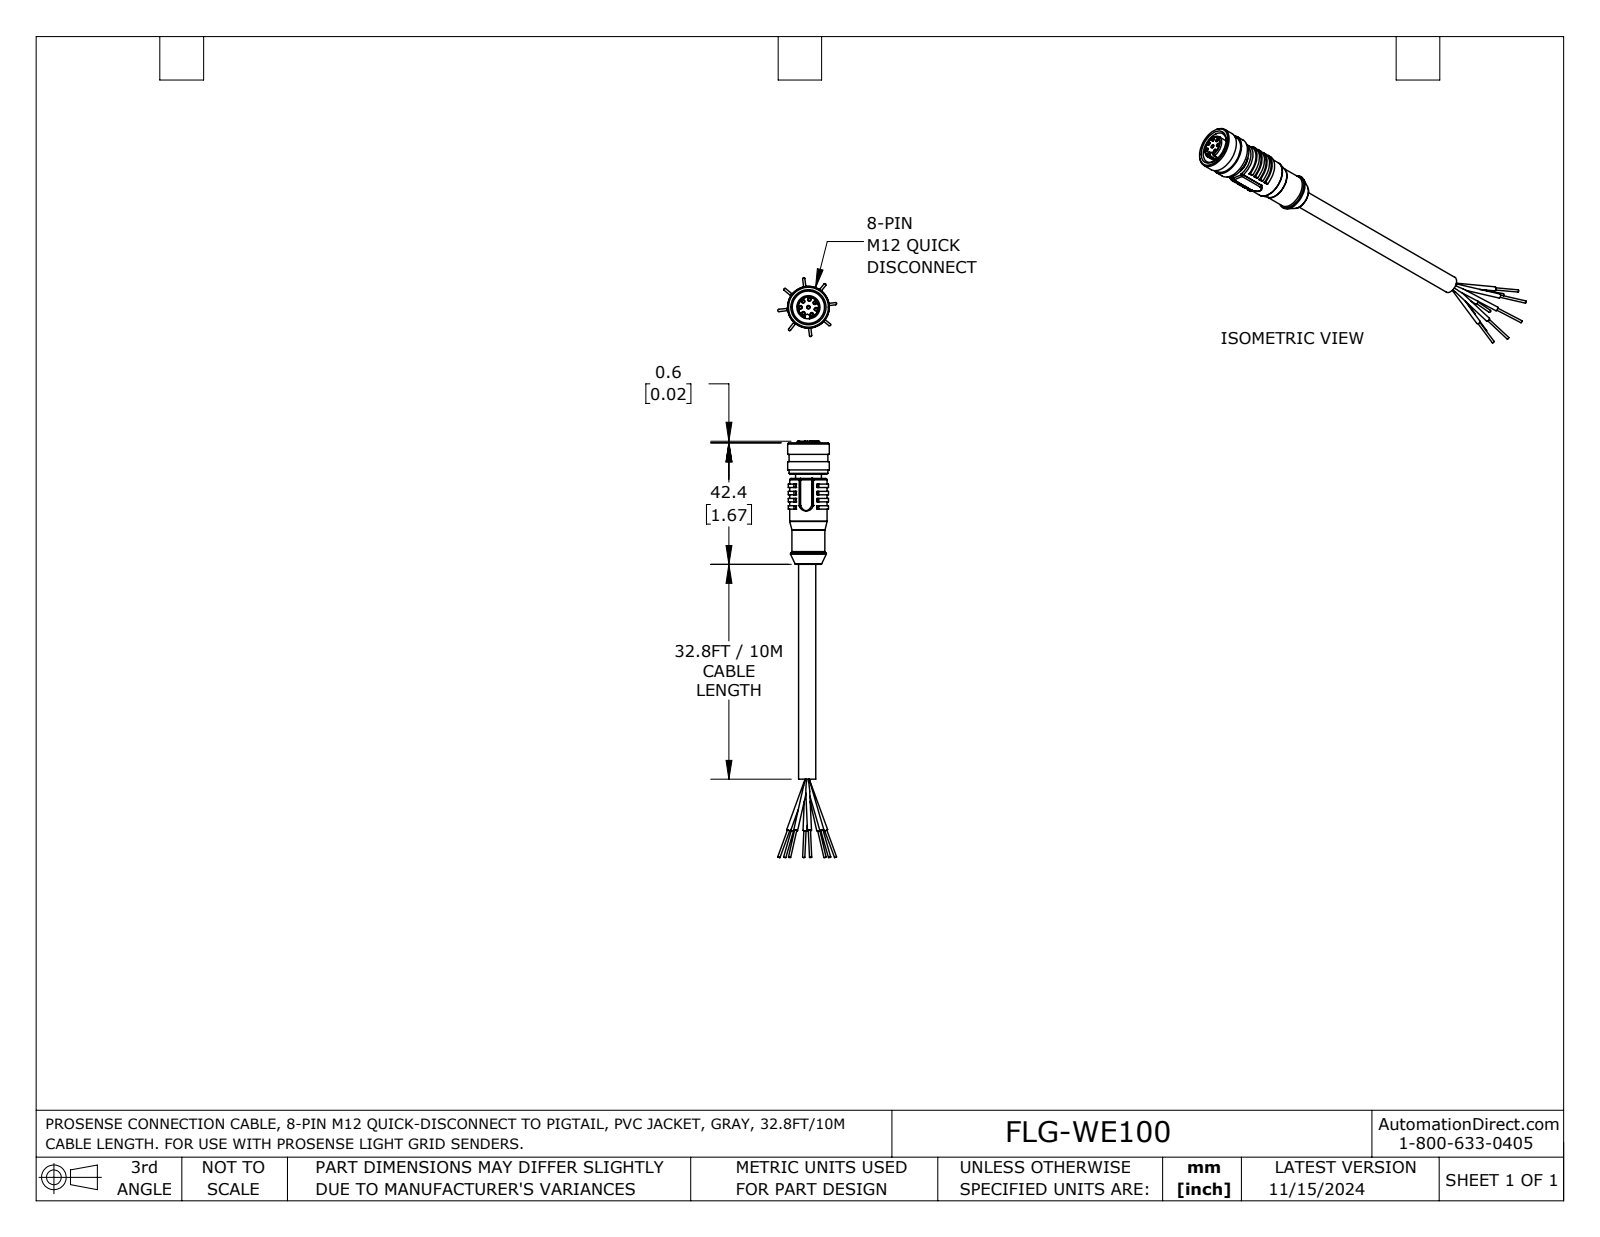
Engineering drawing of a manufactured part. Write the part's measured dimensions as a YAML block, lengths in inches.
part_name: "FLG-WE-CABLE"
step_written_by: "SolidWorks 2023 (AUTOMOTIVE_DESIGN)"
units: inches
bodies: {solids: 1, faces: 183, planar: 73, cylindrical: 61, other: 49}
overall_size: [5.723, 0.81, 0.81]
volume: 0.454
surface_area: 7.833
round_holes:
  - {diameter: 0.034, count: 8}
  - {diameter: 0.443, count: 1}
round_bosses_or_shafts:
  - {diameter: 0.055, count: 8}
  - {diameter: 0.031, count: 8}
  - {diameter: 0.572, count: 1}
  - {diameter: 0.533, count: 1}
  - {diameter: 0.513, count: 1}
  - {diameter: 0.454, count: 1}
  - {diameter: 0.356, count: 1}
  - {diameter: 0.318, count: 1}
partial_cylinders:
  - {radius: 0.02, count: 8}
  - {radius: 0.017, count: 1}
  - {radius: 0.036, count: 1}
  - {radius: 0.099, count: 1}
  - {radius: 0.276, count: 1}
  - {radius: 0.276, count: 1}
face_to_face_distances: [0.098, 0.059, 0.295, 0.197, 0.516, 0.047, 0.193, 0.134, 0.319, 0.394]
hole_center_spacings: [0.09, 0.108, 0.164, 0.109, 0.183, 0.208, 0.214, 0.089]
